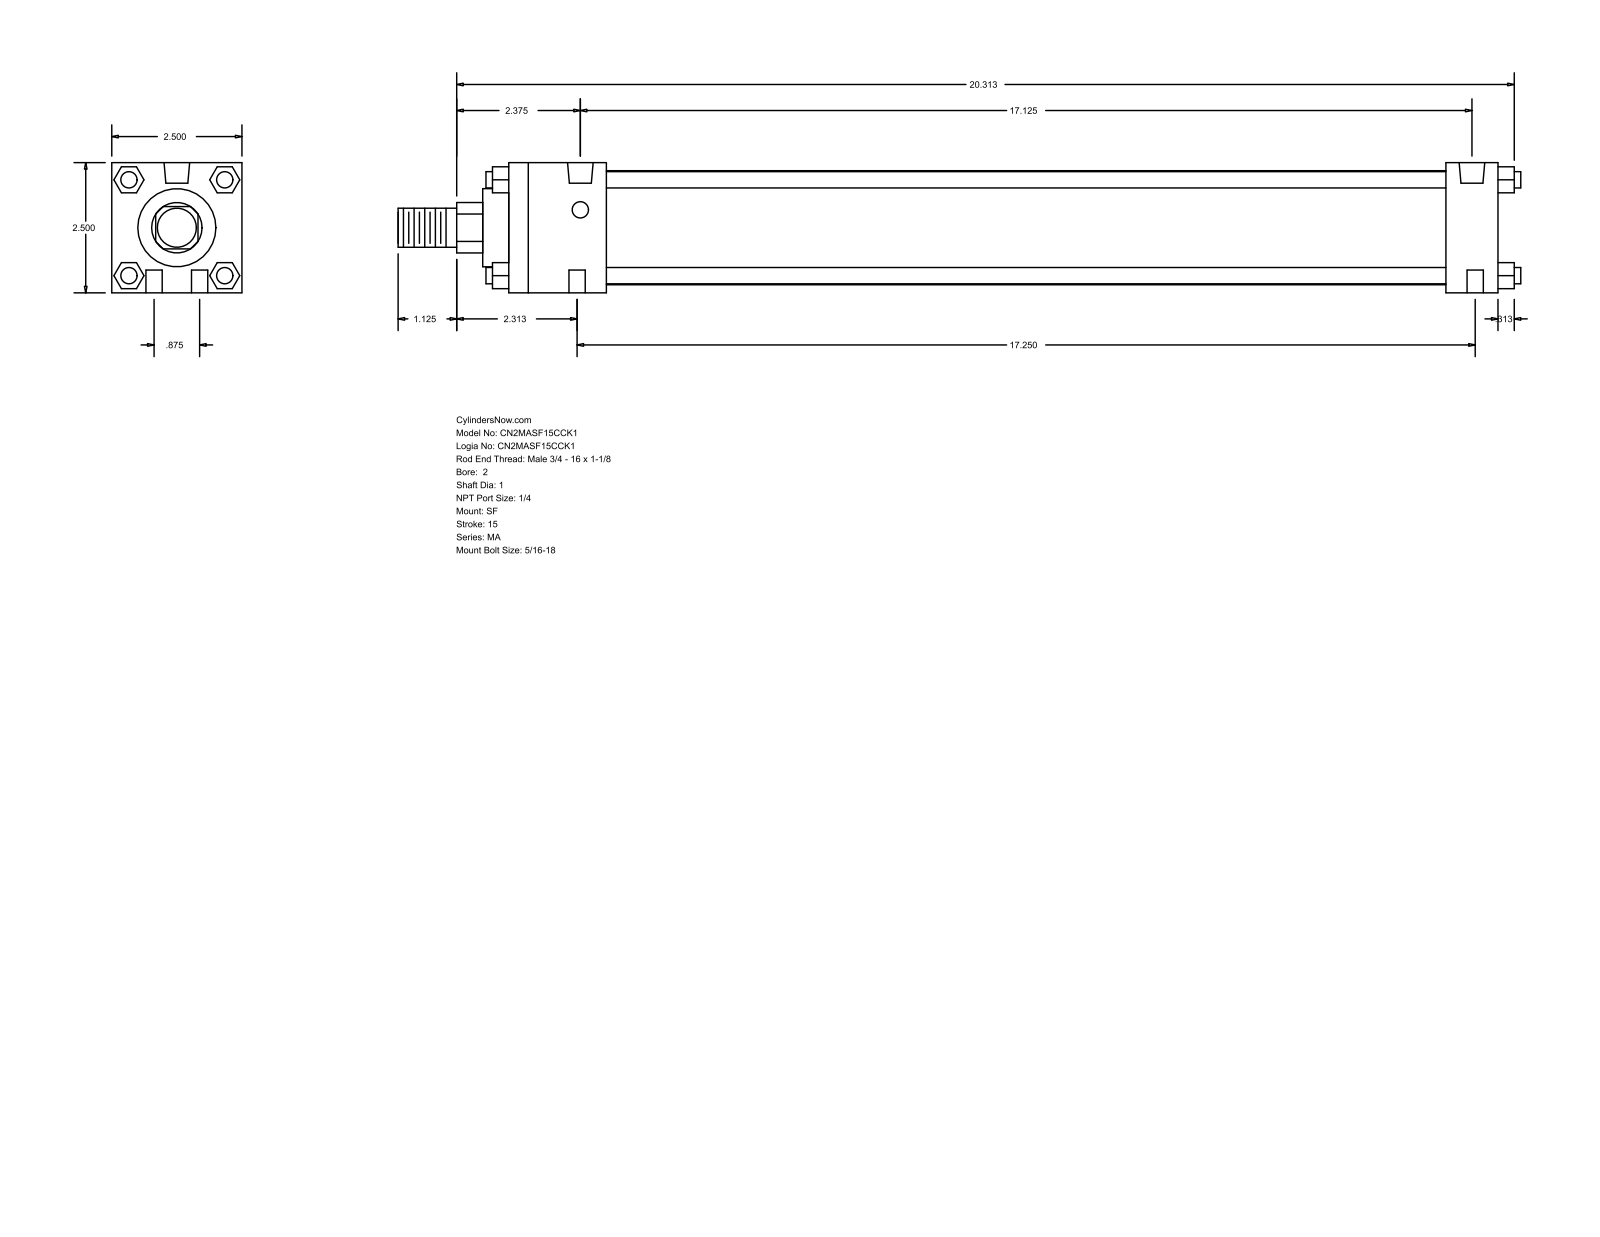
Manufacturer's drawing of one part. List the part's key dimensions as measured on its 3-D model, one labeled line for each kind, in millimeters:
Part name (STEP PRODUCT): MA_SF__0200_1
STEP written by: GSSL Pune (CONFIG_CONTROL_DESIGN)
Units: millimetres
Bodies: 0 solids, 124 faces (94 planar, 30 cylindrical, 0 other)
Overall size (bounding box): 547.69 × 63.5 × 63.5
Round holes (diameter × count): ⌀7.94 ×6, ⌀12.49 ×2
Round bosses / shafts (diameter × count): ⌀7.94 ×4, ⌀55.63 ×1, ⌀38.1 ×1, ⌀25.4 ×1, ⌀19.05 ×1
Partial cylindrical surfaces — rounded edges, fillets, slot ends (radius × count): R12.29 ×1
Main face-to-face distances: 63.5, 482.6, 12.7, 25.4, 457.2, 47.63, 409.57, 434.97, 40.47, 23.37
Hole centre spacings: 11.22, 436.7, 22.22, 434.97, 438.15, 438.71
